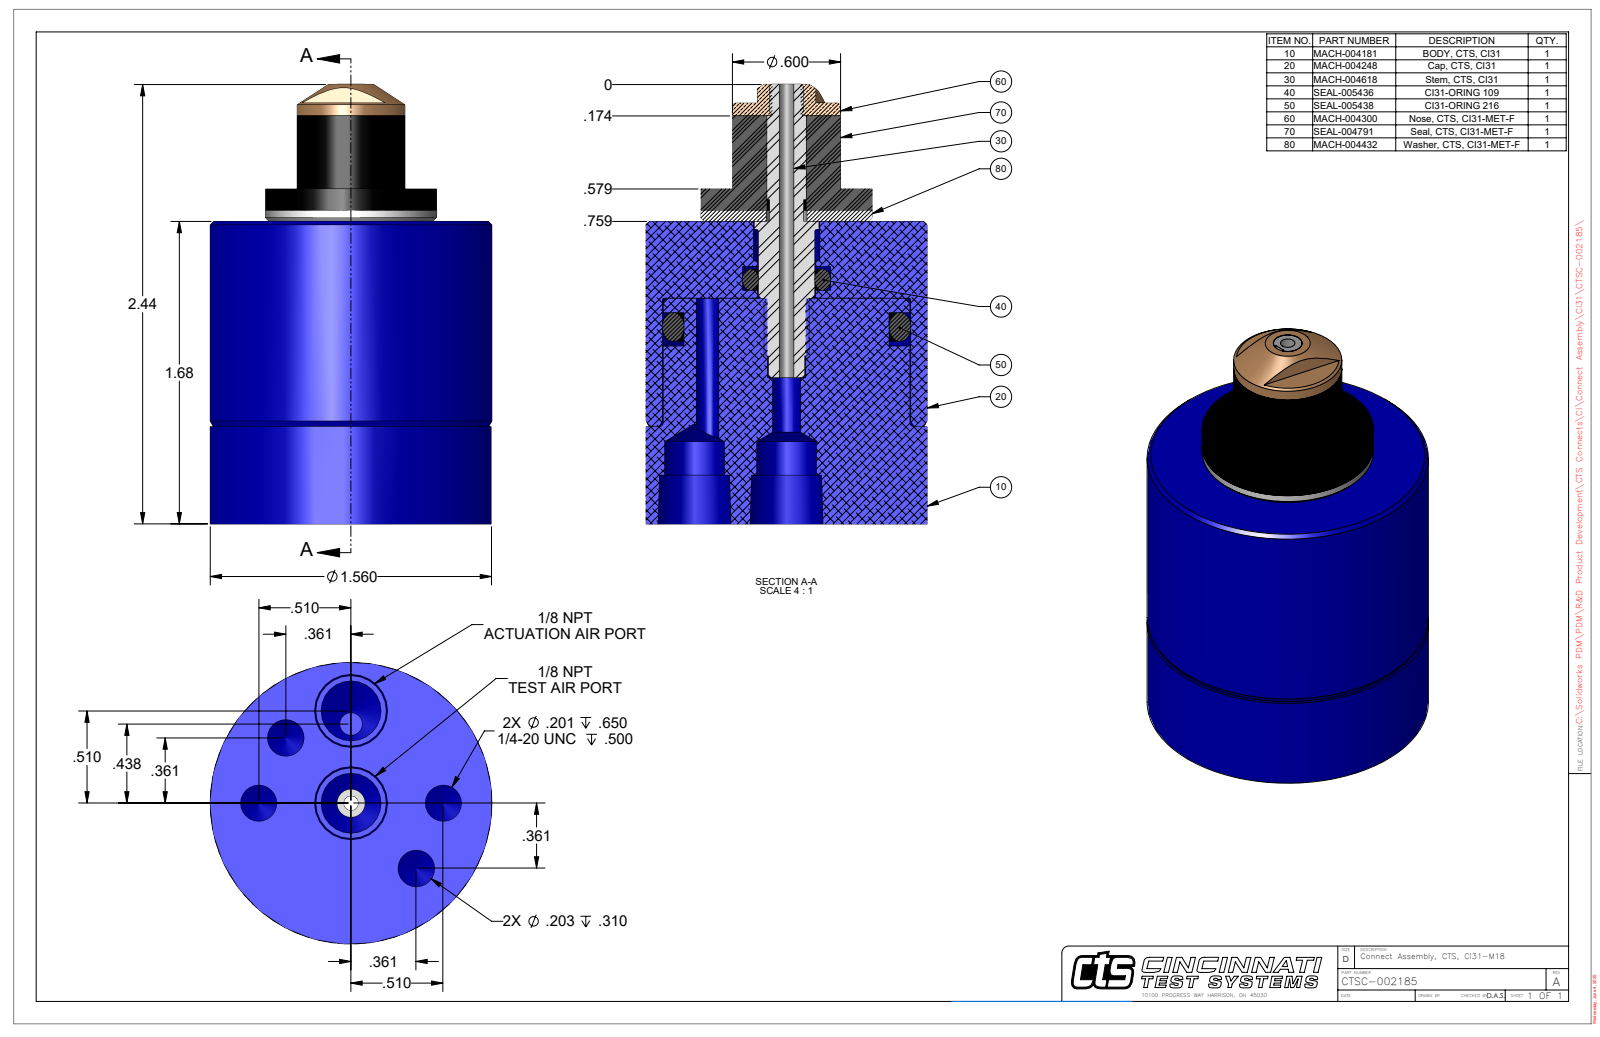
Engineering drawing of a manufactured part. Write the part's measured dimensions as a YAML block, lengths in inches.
part_name: "CTSC-002185"
step_written_by: "SolidWorks 2023 (AUTOMOTIVE_DESIGN)"
units: inches
bodies: {solids: 1, faces: 87, planar: 22, cylindrical: 35, other: 30}
overall_size: [2.437, 1.56, 1.56]
volume: 3.282
surface_area: 19.12
round_holes:
  - {diameter: 0.201, count: 2}
  - {diameter: 0.203, count: 2}
  - {diameter: 0.332, count: 2}
  - {diameter: 0.081, count: 1}
  - {diameter: 0.125, count: 1}
  - {diameter: 0.156, count: 1}
  - {diameter: 0.368, count: 1}
  - {diameter: 1.377, count: 1}
round_bosses_or_shafts:
  - {diameter: 1.56, count: 1}
  - {diameter: 1.365, count: 1}
  - {diameter: 0.95, count: 1}
  - {diameter: 0.6, count: 1}
  - {diameter: 0.357, count: 1}
partial_cylinders:
  - {radius: 0.079, count: 1}
face_to_face_distances: [1.677, 1.857, 0.18, 0.542, 1.135, 1.315, 2.332, 1.79, 0.655, 0.475]
hole_center_spacings: [0.51, 0.39, 0.942, 0.672, 0.721, 0.072, 0.369, 0.437]
